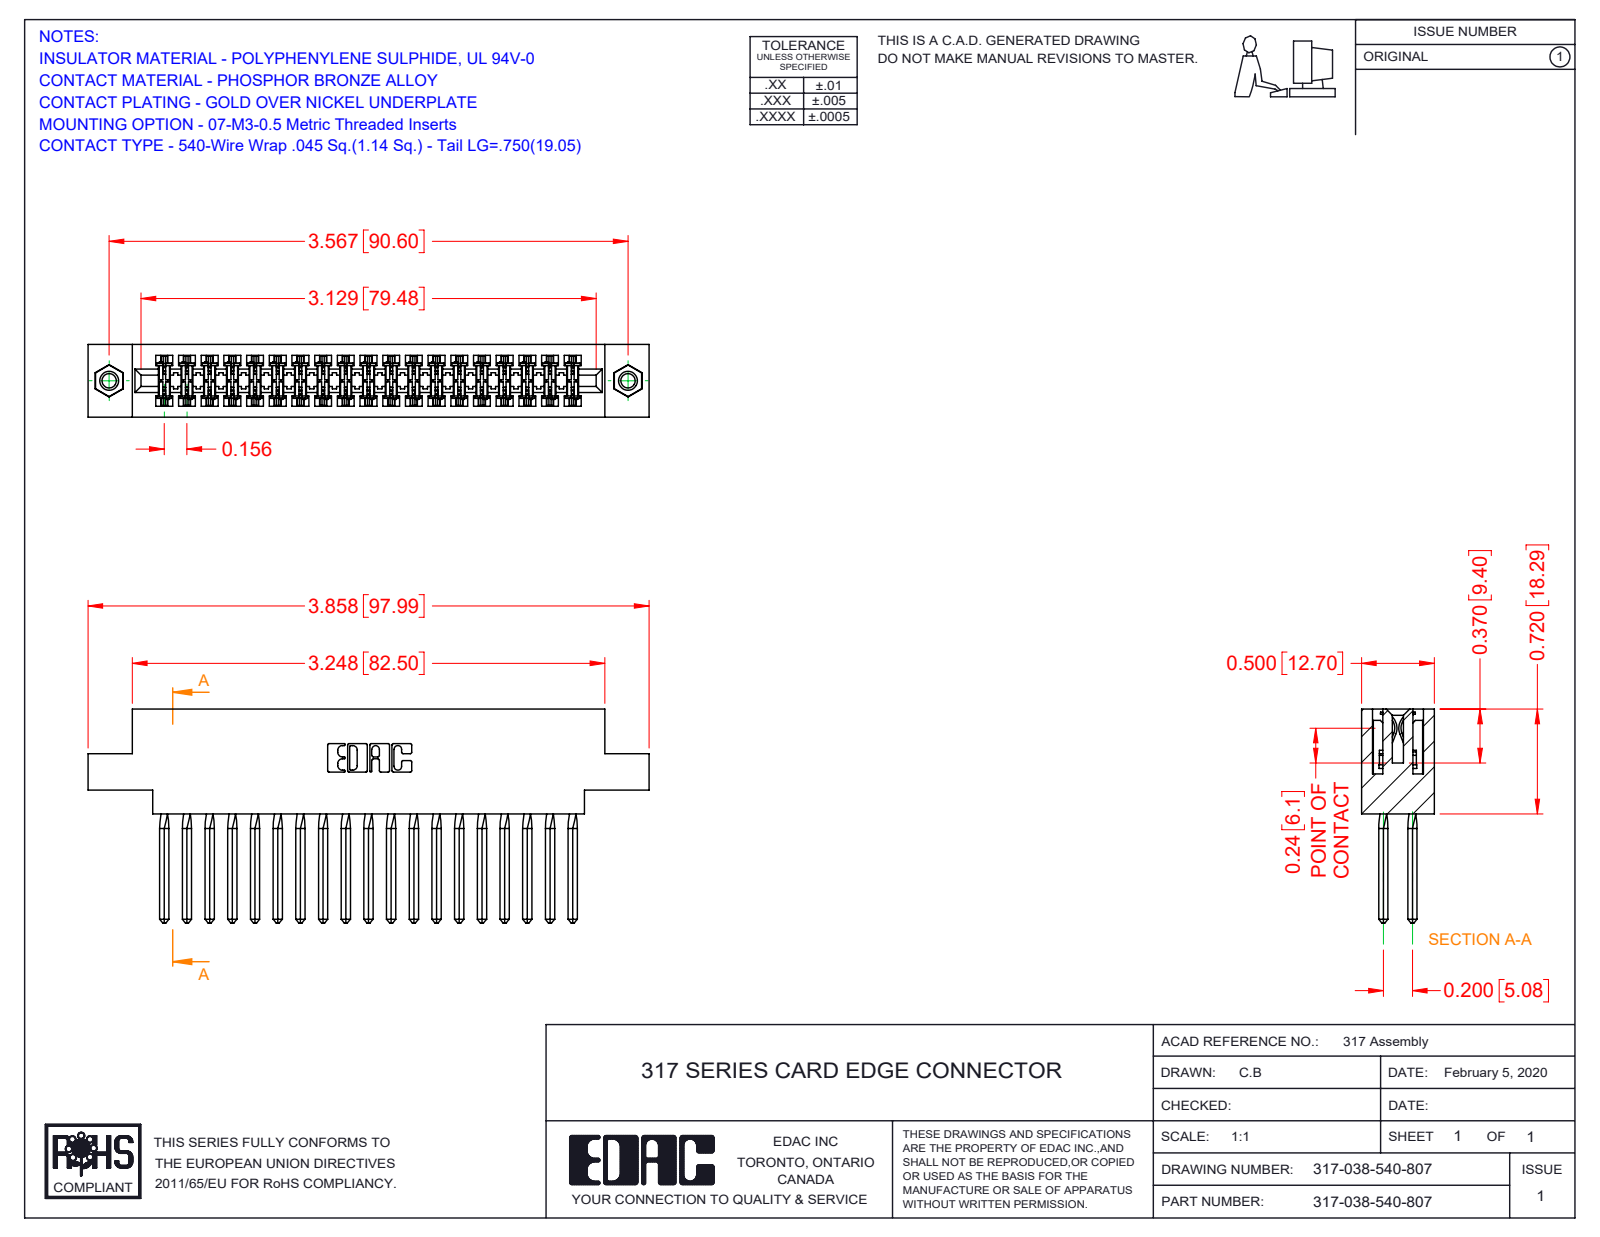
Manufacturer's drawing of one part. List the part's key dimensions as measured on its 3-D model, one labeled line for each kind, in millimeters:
Part name (STEP PRODUCT): 345-250-001_345-250-005-103; 317-038-540-807; 317 Part_.156 Dia - TI; 317-290-001_540
STEP written by: SolidWorks 2016 (CONFIG_CONTROL_DESIGN)
Units: millimetres
Bodies: 41 solids, 3544 faces (2864 planar, 512 cylindrical, 168 other)
Overall size (bounding box): 98 × 37.3 × 12.7
Volume: 15 600 mm³ · Surface area: 22 510 mm²
Round holes (diameter × count): ⌀2.5 ×2, ⌀3.2 ×2, ⌀4 ×2
Round bosses / shafts (diameter × count): ⌀3.9 ×2
Partial cylindrical surfaces — rounded edges, fillets, slot ends (radius × count): R0.4 ×76, R0.3 ×22, R0.2 ×6, R0.8 ×6, R0.7 ×3, R2.4 ×2, R2.5 ×2, R2.8 ×2
Main face-to-face distances: 12.7, 1.9, 10.8, 2.8, 8.9, 5, 5.6, 18.3, 3.5, 2.4
Hole centre spacings: 90.6
